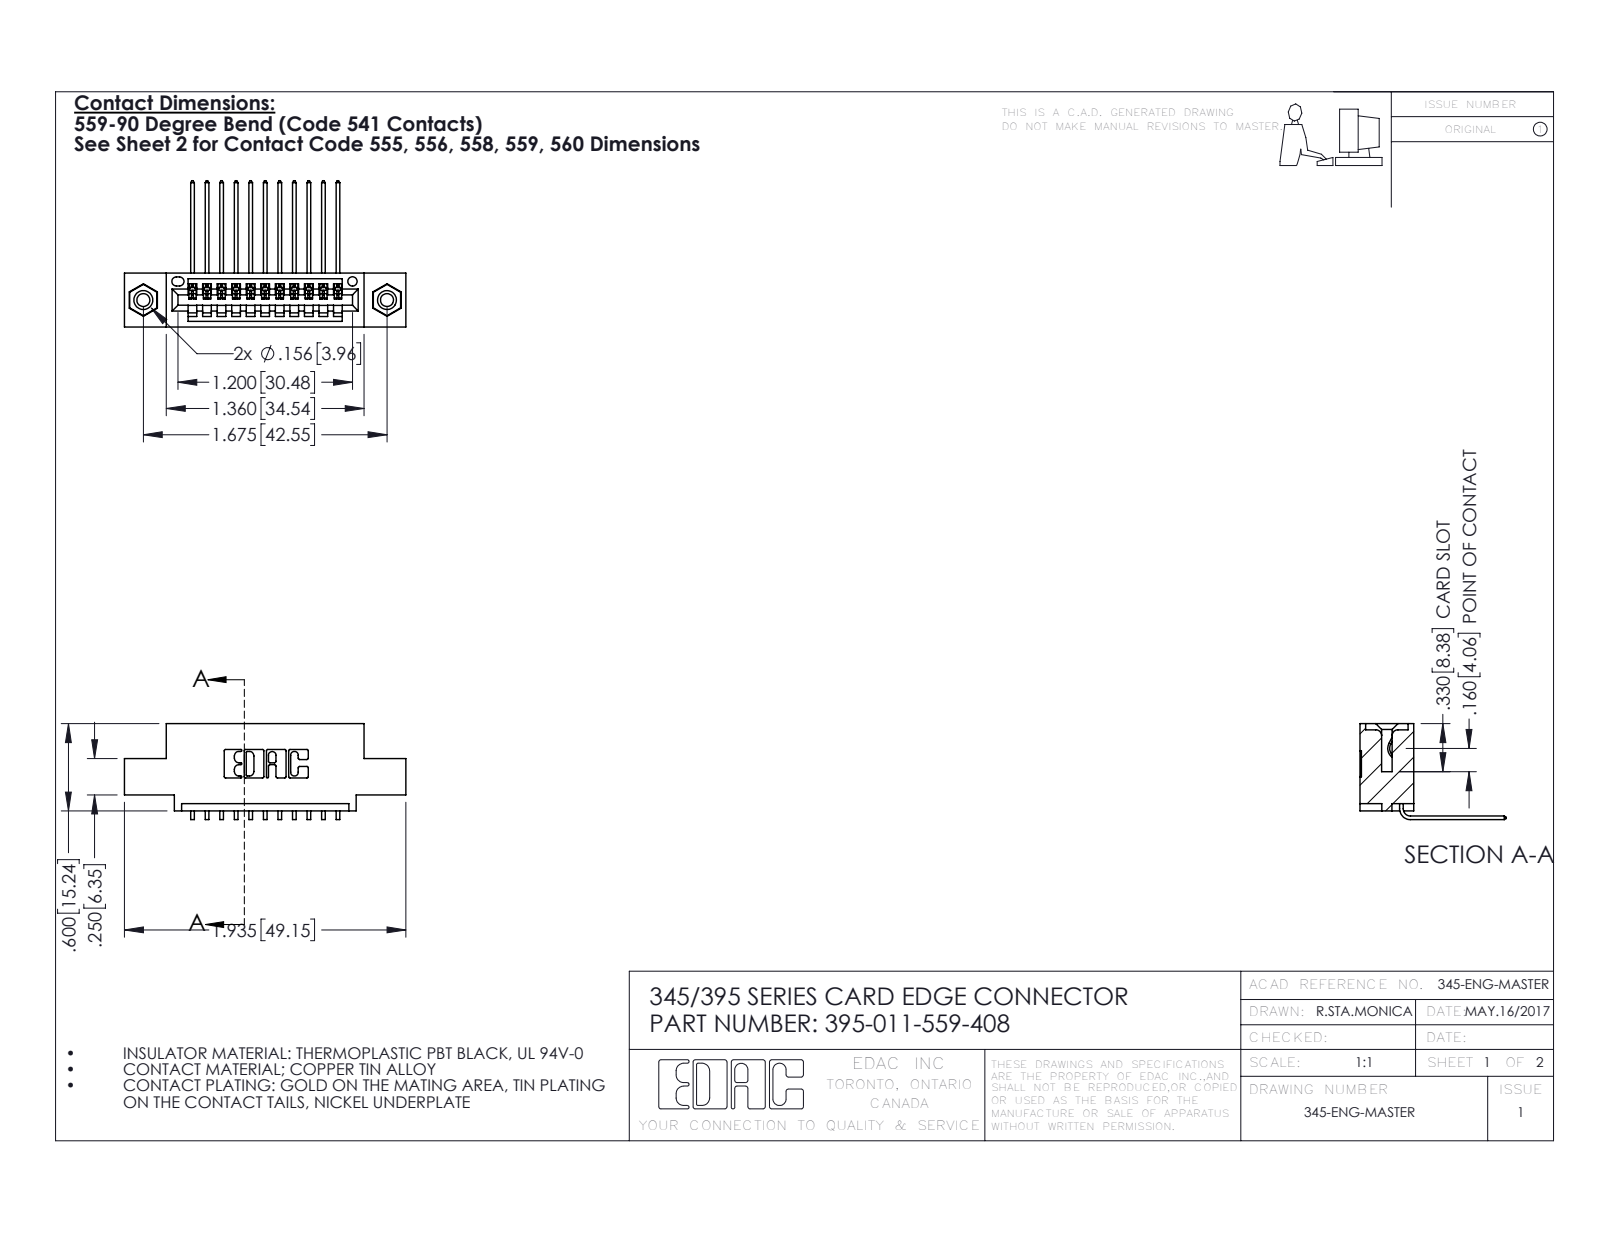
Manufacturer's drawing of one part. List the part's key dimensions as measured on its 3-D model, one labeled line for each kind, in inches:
Part name (STEP PRODUCT): 345-250-001_345-250-003-102; 345 Part_0.110 Offset - 0.156 Dia-TI; 395-011-559-408; 345-292-001_558 559 Tail - 1
STEP written by: SolidWorks 2016 (CONFIG_CONTROL_DESIGN)
Units: inches
Bodies: 14 solids, 850 faces (578 planar, 256 cylindrical, 16 other)
Overall size (bounding box): 1.935 × 1.005 × 0.659
Volume: 0.267 in³ · Surface area: 8.841 in²
Round holes (diameter × count): ⌀0.089 ×2, ⌀0.125 ×2, ⌀0.156 ×2, ⌀0.064 ×1
Round bosses / shafts (diameter × count): ⌀0.155 ×2
Partial cylindrical surfaces — rounded edges, fillets, slot ends (radius × count): R0.006 ×22, R0.01 ×22, R0.007 ×6, R0.031 ×6, R0.026 ×3, R0.031 ×2, R0.04 ×2, R0.014 ×1
Main face-to-face distances: 0.2, 0.072, 0.298, 0.37, 0.098, 0.272, 0.025, 0.1, 0.6, 0.06
Hole centre spacings: 0.27, 1.443, 1.675
